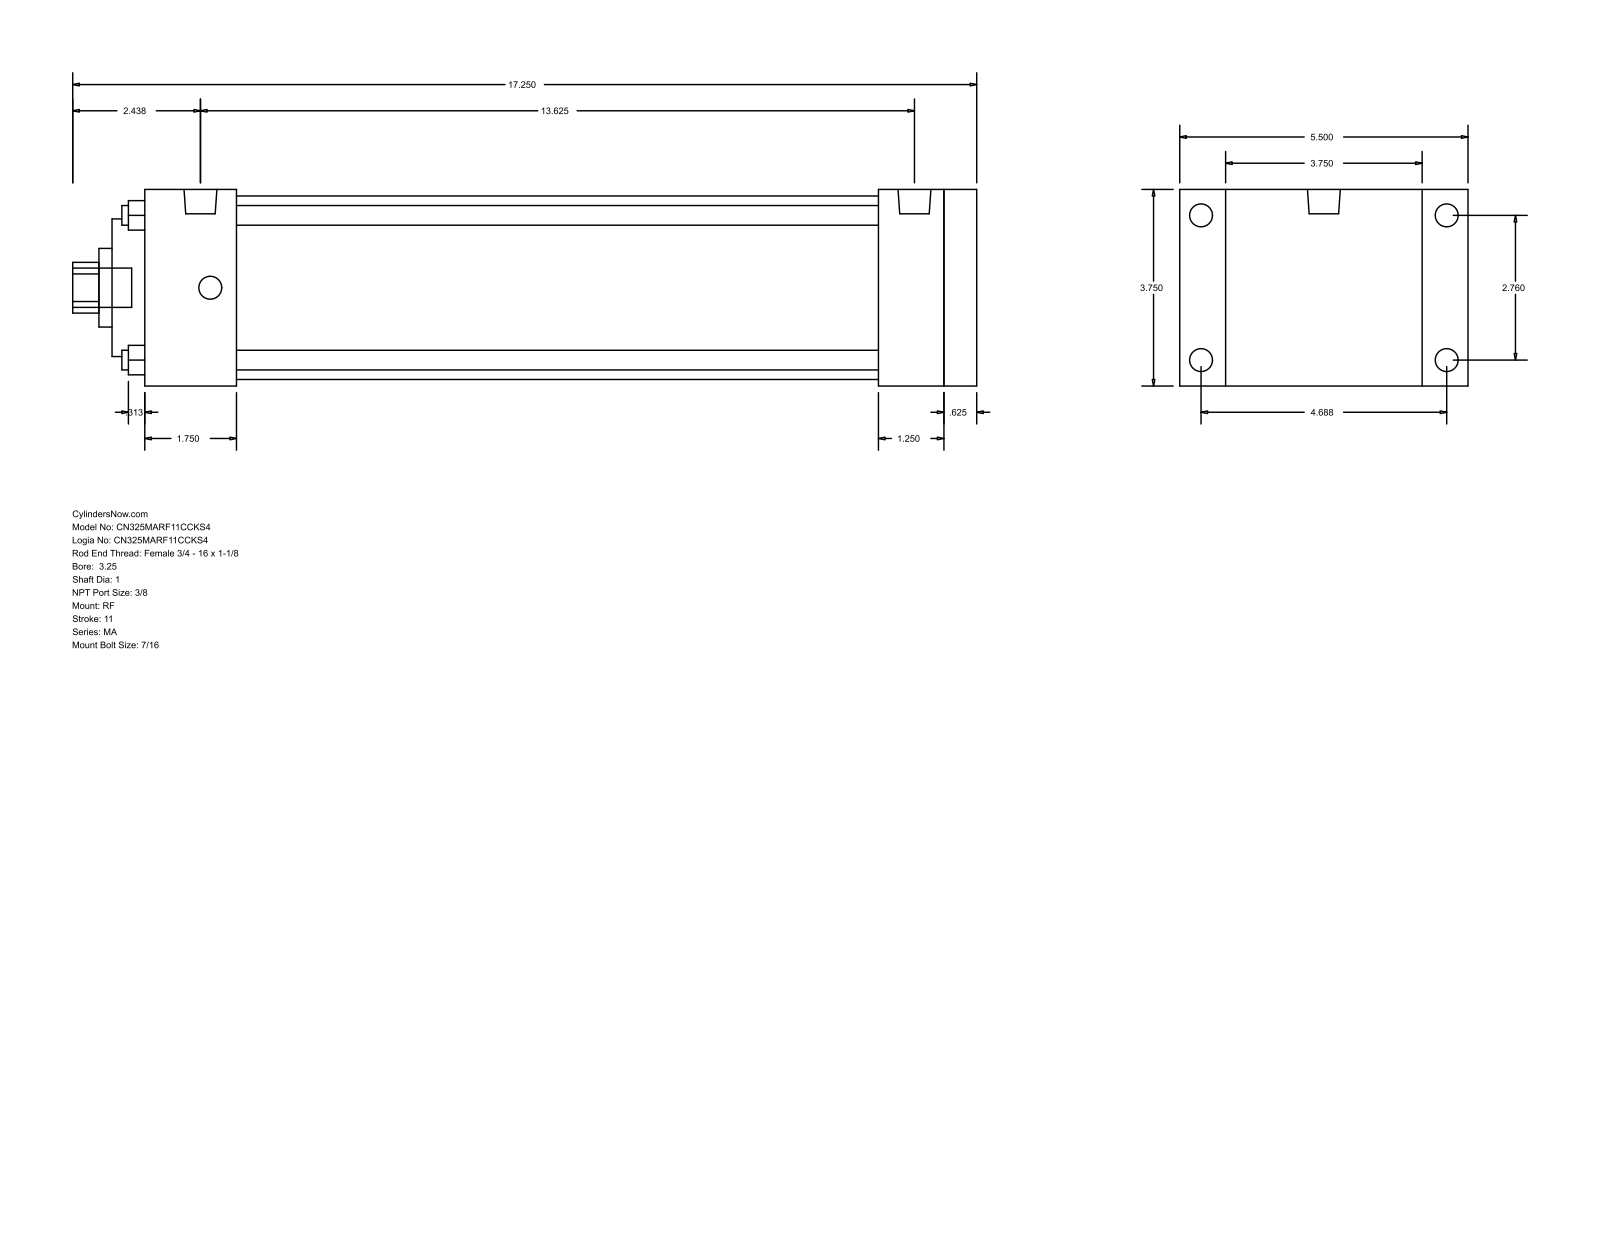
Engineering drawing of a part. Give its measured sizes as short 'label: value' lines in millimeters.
name: MA_RF__0325_1
written by: GSSL Pune (CONFIG_CONTROL_DESIGN)
unit: mm
bodies: 0 solids, 94 faces (65 planar, 29 cylindrical, 0 other)
size: 438.15 × 139.7 × 95.25
holes: 4× ⌀9.53, 1× ⌀25.4, 1× ⌀38.1, 1× ⌀66.67, 1× ⌀88.9
bosses: 8× ⌀11.11, 2× ⌀15.93, 1× ⌀19.05
rounds: 1× R12.29
face distances: 95.24, 403.23, 387.35, 15.88, 22.23, 117.47, 15.87, 355.6, 31.75, 47.63
hole spacings: 49.57, 70.1, 99.14
